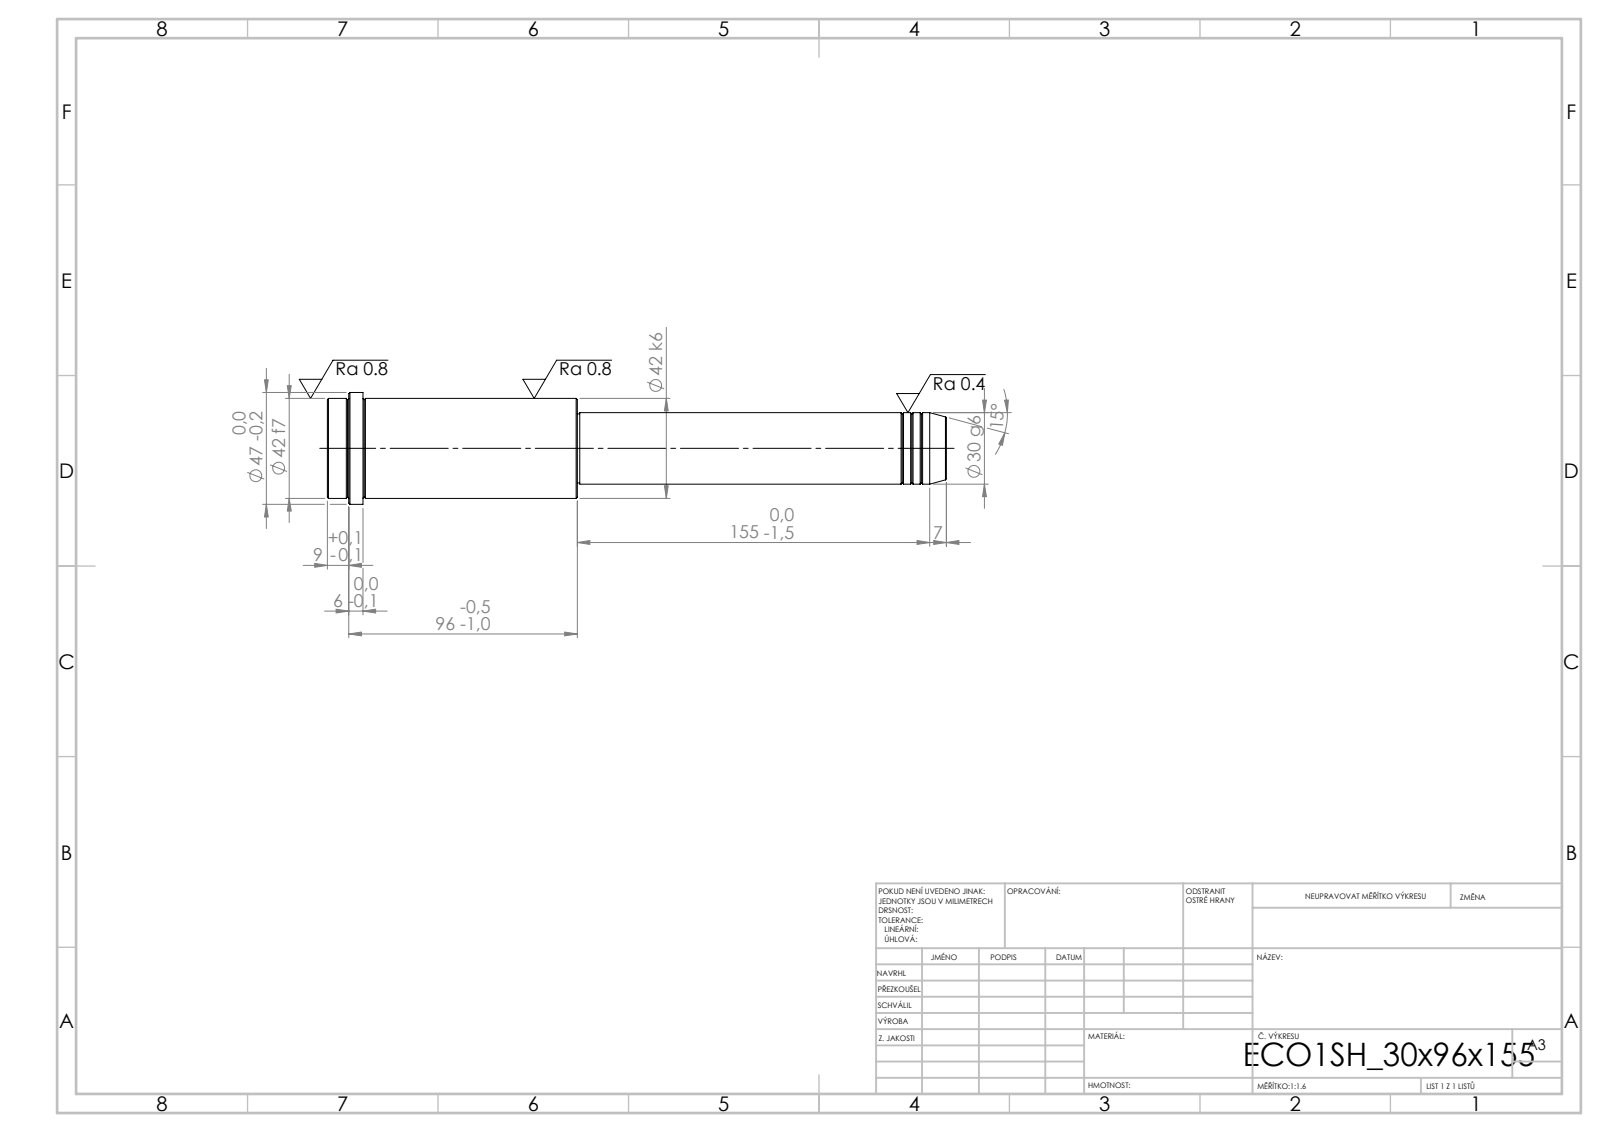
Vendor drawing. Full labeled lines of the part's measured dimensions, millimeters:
STEP written by: SolidWorks 2019 (CONFIG_CONTROL_DESIGN)
Units: millimetres
Bodies: 1 solid, 52 faces (6 planar, 16 cylindrical, 30 other)
Overall size (bounding box): 260 × 47 × 47
Volume: 256 227 mm³ · Surface area: 32 097 mm²
Round bosses / shafts (diameter × count): ⌀47 ×1, ⌀42 ×1, ⌀30 ×1, ⌀29 ×1
Main face-to-face distances: 105, 155, 260, 245, 90, 15, 251, 96, 6, 9
